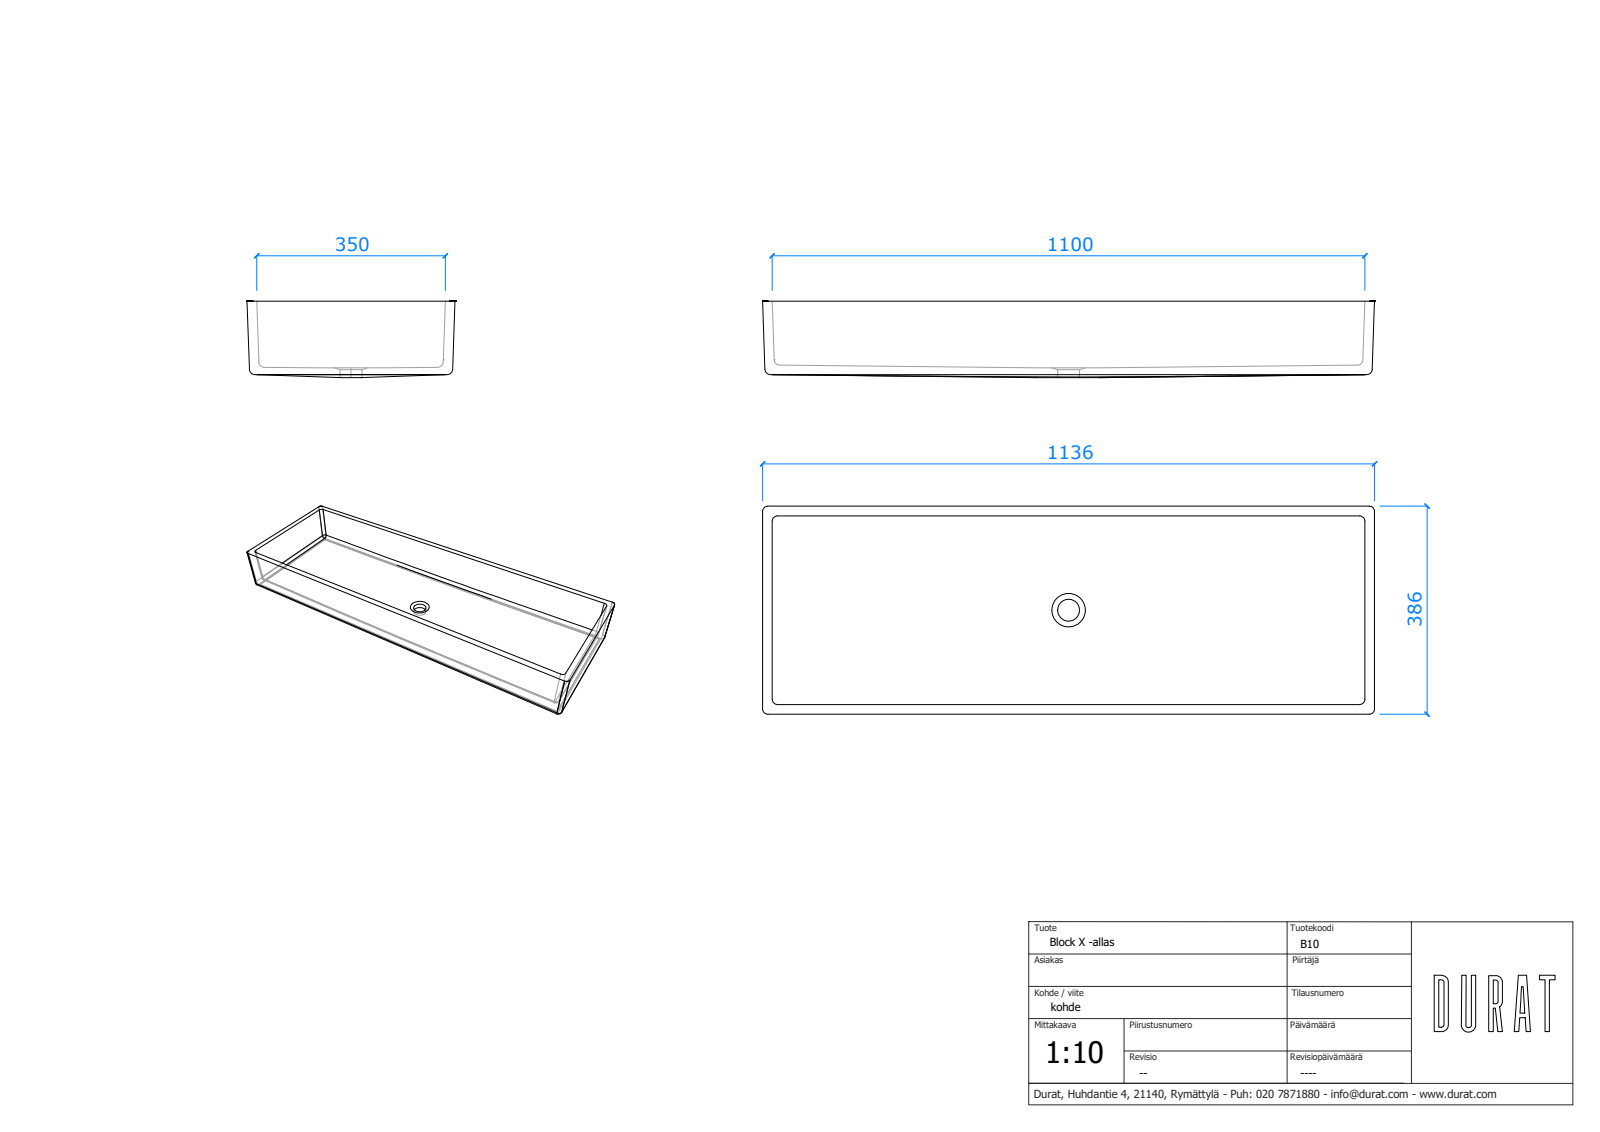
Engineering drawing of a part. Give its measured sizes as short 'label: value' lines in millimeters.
written by: ST-DEVELOPER v15 (AUTOMOTIVE_DESIGN)
unit: mm
bodies: 0 solids, 48 faces (16 planar, 0 cylindrical, 32 other)
size: 1136.02 × 386.02 × 141.5
face distances: 17.97, 18.01, 18, 17.98, 136, 5.5, 141.5, 12.5, 123.5, 350
